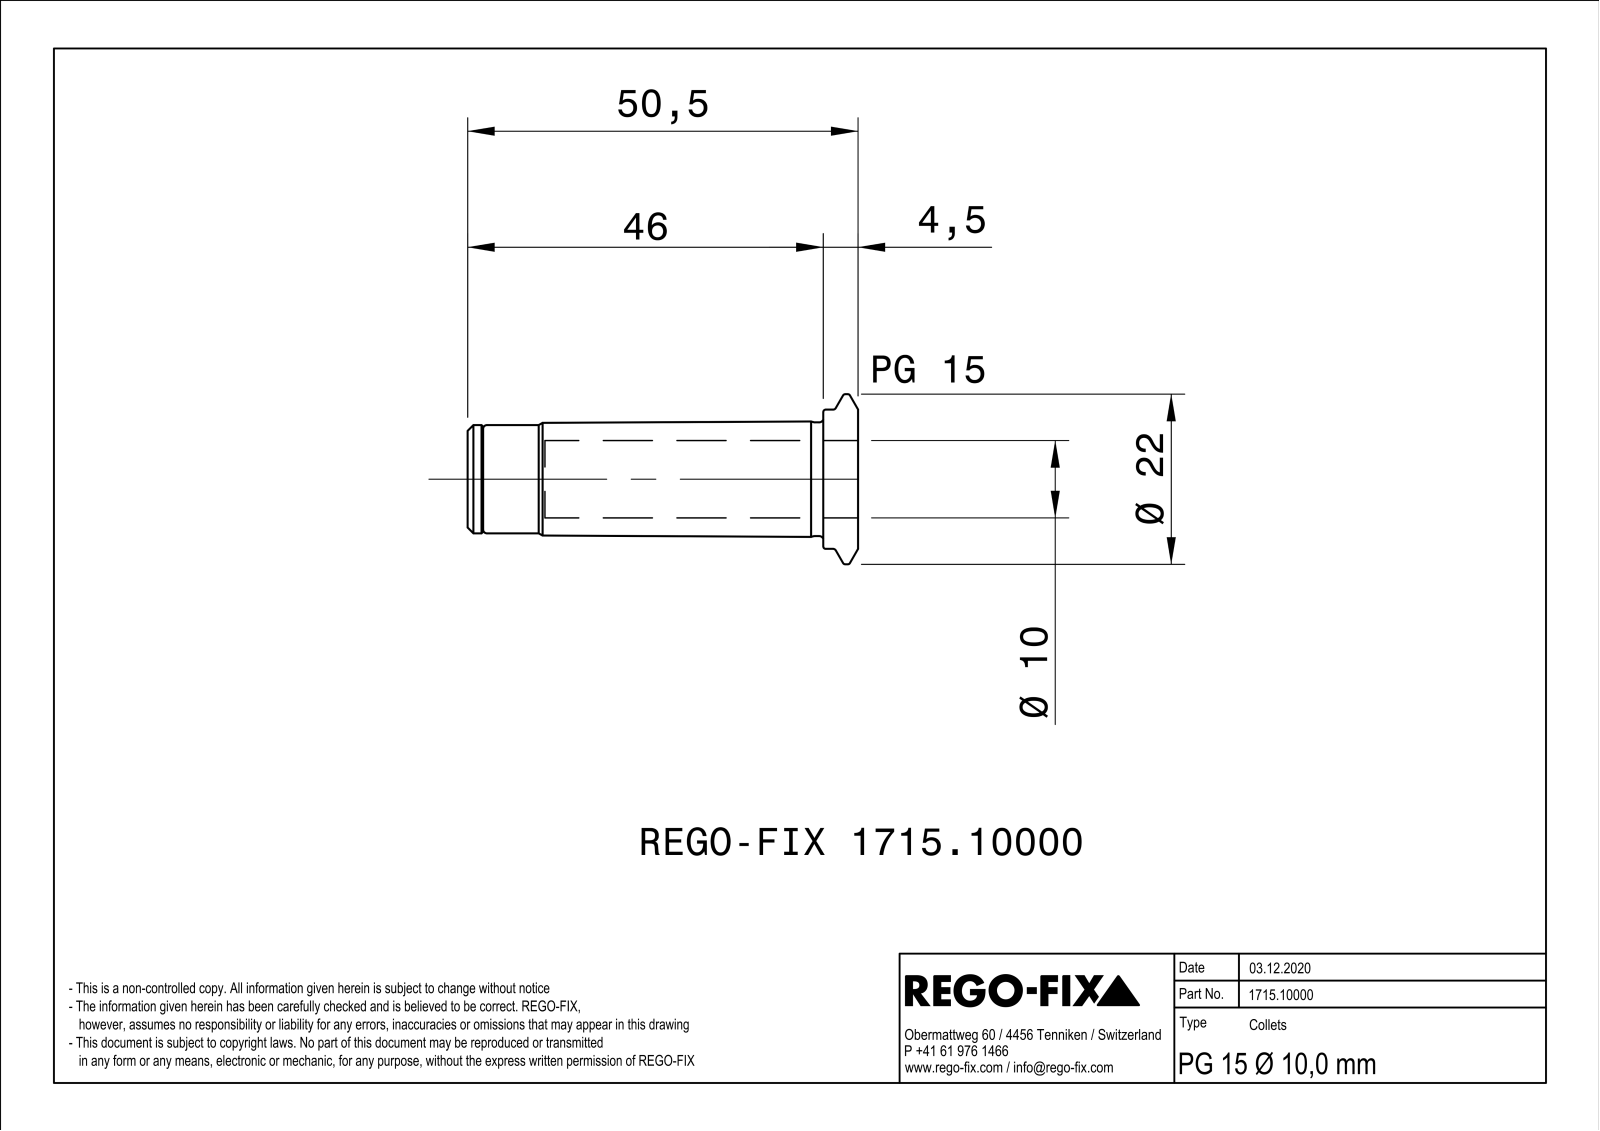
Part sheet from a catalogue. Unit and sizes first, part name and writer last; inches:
Units: inches
Overall size (bounding box): 1.988 × 0.866 × 0.866
Round holes (diameter × count): ⌀0.205 ×1, ⌀0.272 ×1, ⌀0.323 ×1, ⌀0.394 ×1, ⌀0.43 ×1, ⌀0.48 ×1
Round bosses / shafts (diameter × count): ⌀0.866 ×1, ⌀0.709 ×1, ⌀0.579 ×1, ⌀0.551 ×1
Partial cylindrical surfaces — rounded edges, fillets, slot ends (radius × count): R0.02 ×6, R0.205 ×1, R0.236 ×1
Main face-to-face distances: 0.039, 0.079, 1.988, 1.594, 0.394, 1.634, 0.354, 0.118, 0.177, 1.417
Bodies: 0 solids, 115 faces (35 planar, 31 cylindrical, 49 other)
Part name (STEP PRODUCT): NOCUT
STEP written by: SIEMENS PLM Software Solid Edge ST10 (AUTOMOTIVE_DESIGN)
